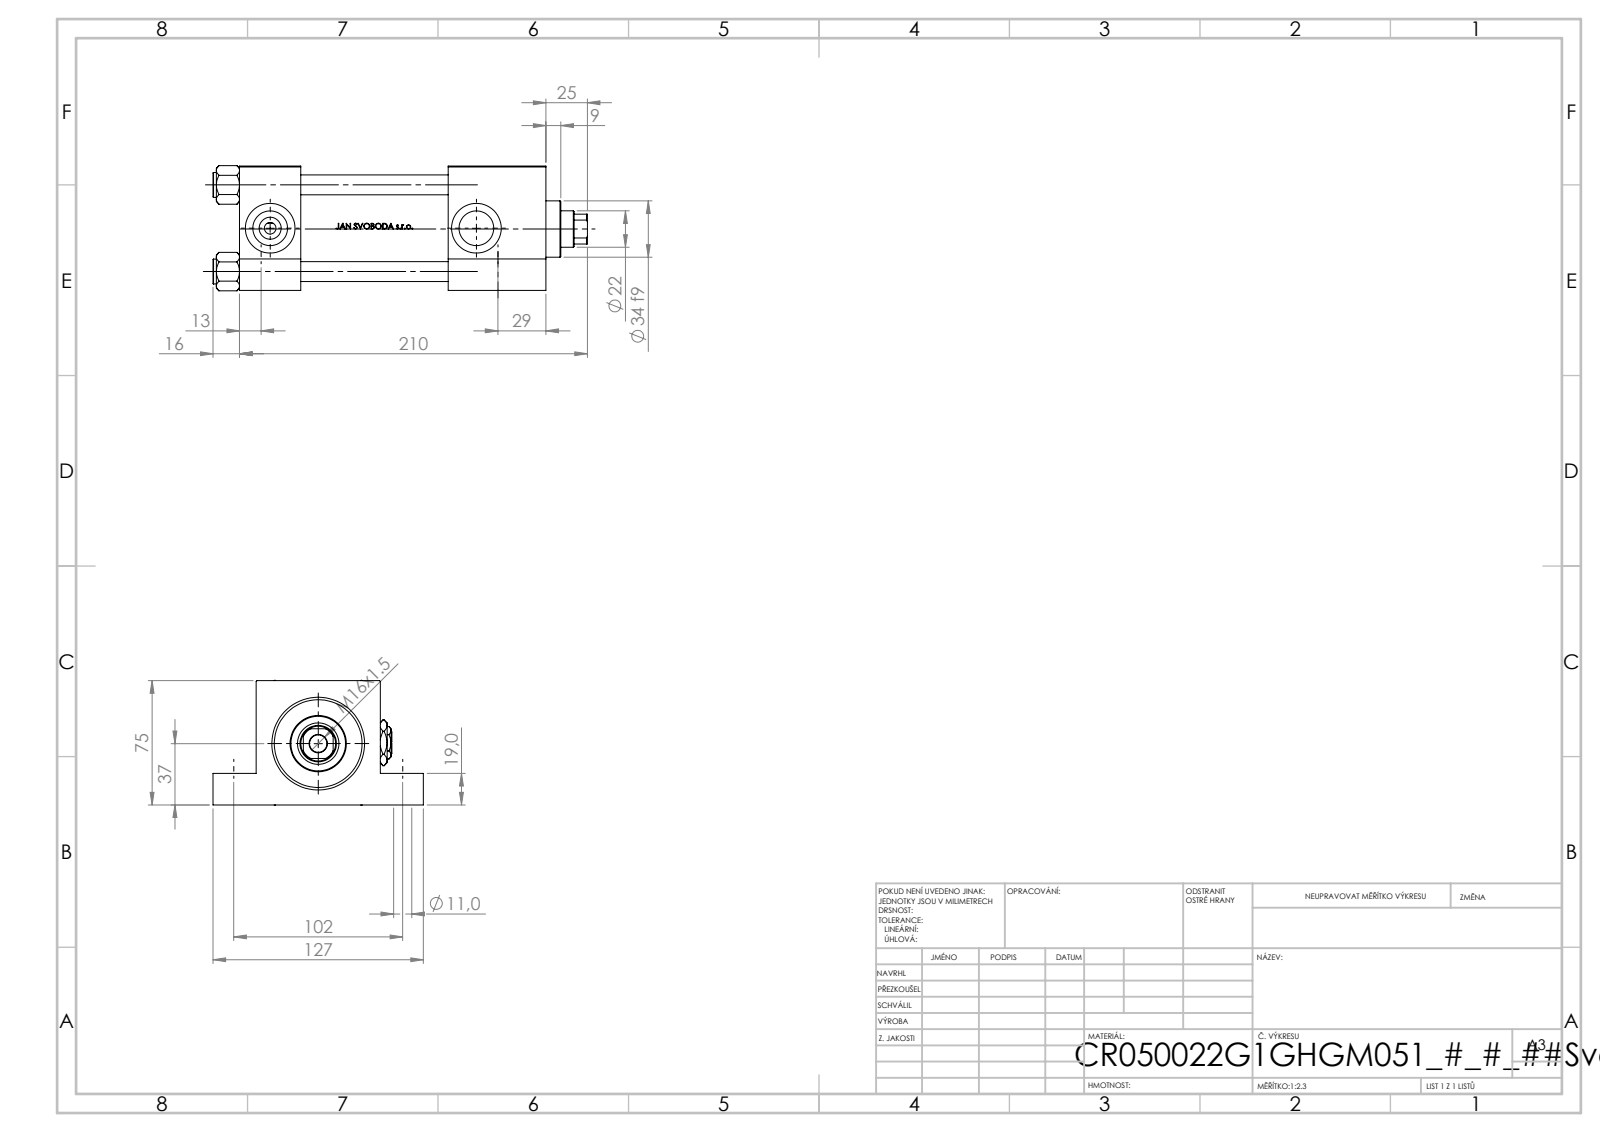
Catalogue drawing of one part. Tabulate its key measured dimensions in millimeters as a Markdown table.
| quantity | value |
| --- | --- |
| part name | Zatka_pro_OIL_PORT; V215CR_VCP_G; V215CR_G_Body; NUT_M5_G (+2 more) |
| STEP written by | SolidWorks 2019 (CONFIG_CONTROL_DESIGN) |
| units | millimeters |
| bodies | 12 solids, 1134 faces (454 planar, 128 cylindrical, 552 other) |
| overall size | 226 × 127 × 75.54 |
| volume | 793 696 mm³ |
| surface area | 178 444 mm² |
| round holes (diameter × count) | 11 × 4, 12 × 4, 7 × 2, 20.96 × 2, 30 × 2, 10.5 × 1, 22 × 1, 25 × 1, 41 × 1, 50 × 1, 53 × 1 |
| round bosses / shafts (diameter × count) | 15 × 4, 56 × 1, 34 × 1 |
| partial cylindrical surfaces (radius × count) | 10.5 × 1 |
| main face-to-face distances | 75, 37, 185, 148, 89, 19, 56, 126, 59, 26 |
| hole center spacings | 52.3, 36.63, 37.34, 73.96, 102, 143, 175.65, 124.5 |
